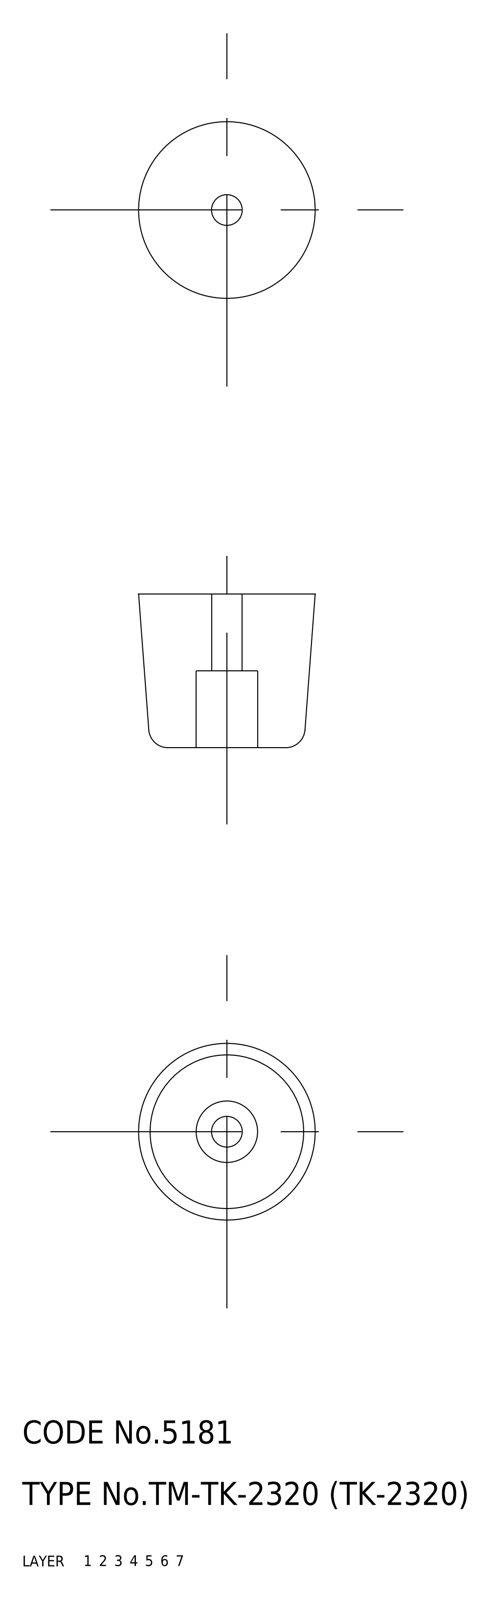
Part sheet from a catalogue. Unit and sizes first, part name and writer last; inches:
Units: inches
Overall size (bounding box): 0.906 × 0.906 × 0.787
Volume: 0.402 in³ · Surface area: 4.058 in²
Bodies: 2 solids, 20 faces (0 planar, 0 cylindrical, 20 other)
Part name (STEP PRODUCT): washer; rubber foot; TK_2320_9444_36
STEP written by: CADfix (AUTOMOTIVE_DESIGN)
